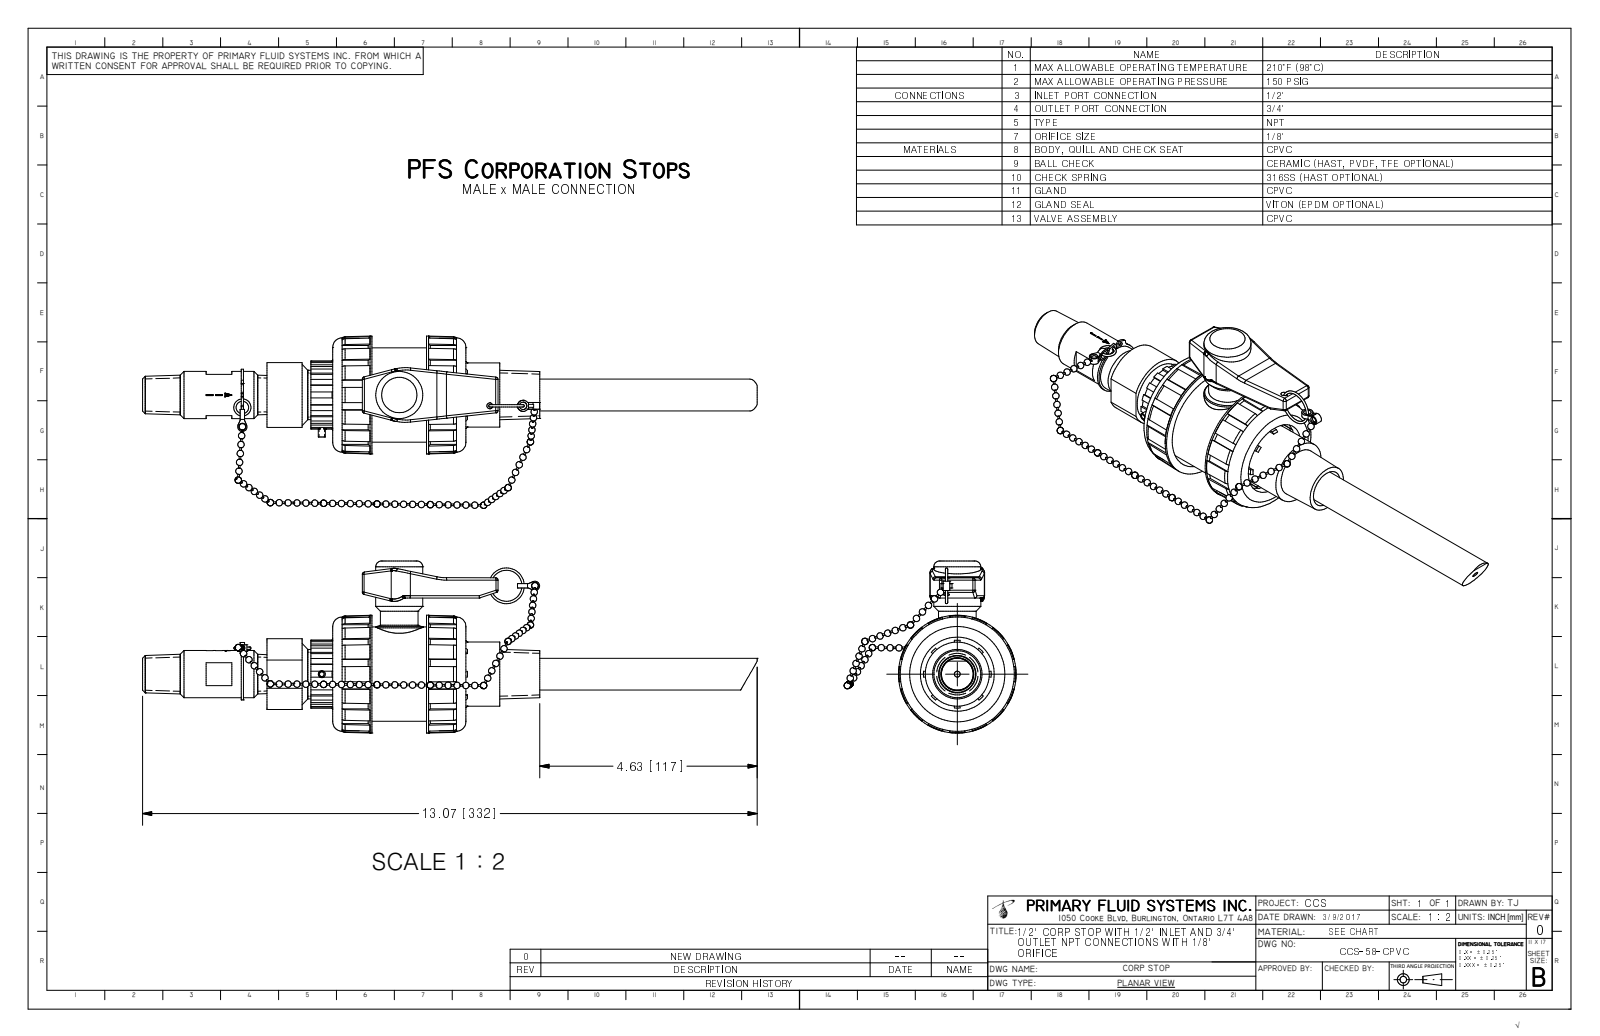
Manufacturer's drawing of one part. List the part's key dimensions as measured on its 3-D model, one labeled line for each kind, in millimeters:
Part name (STEP PRODUCT): CCS-58-CPVC_R0
STEP written by: Autodesk Inventor 2009 (AUTOMOTIVE_DESIGN)
Units: millimetres
Bodies: 1 solid, 618 faces (224 planar, 147 cylindrical, 247 other)
Overall size (bounding box): 332 × 92.9 × 92.7
Volume: 313 200 mm³ · Surface area: 71 230 mm²
Round holes (diameter × count): ⌀2 ×1, ⌀3.2 ×1, ⌀6.4 ×1, ⌀11.9 ×1, ⌀14.2 ×1, ⌀39.9 ×1, ⌀54.9 ×1
Round bosses / shafts (diameter × count): ⌀25.4 ×2, ⌀63.5 ×1, ⌀50.8 ×1, ⌀45.7 ×1, ⌀34.5 ×1, ⌀27.8 ×1, ⌀20.3 ×1, ⌀17.1 ×1
Partial cylindrical surfaces — rounded edges, fillets, slot ends (radius × count): R1.3 ×21, R25.4 ×3, R1.1 ×2, R4 ×2, R8.9 ×1, R11.6 ×1, R11.8 ×1, R12.7 ×1
Main face-to-face distances: 5.2, 66.7, 21.2, 50.7, 16, 45.5, 11.8, 71.9, 61.5, 29.5
Hole centre spacings: 14.3
